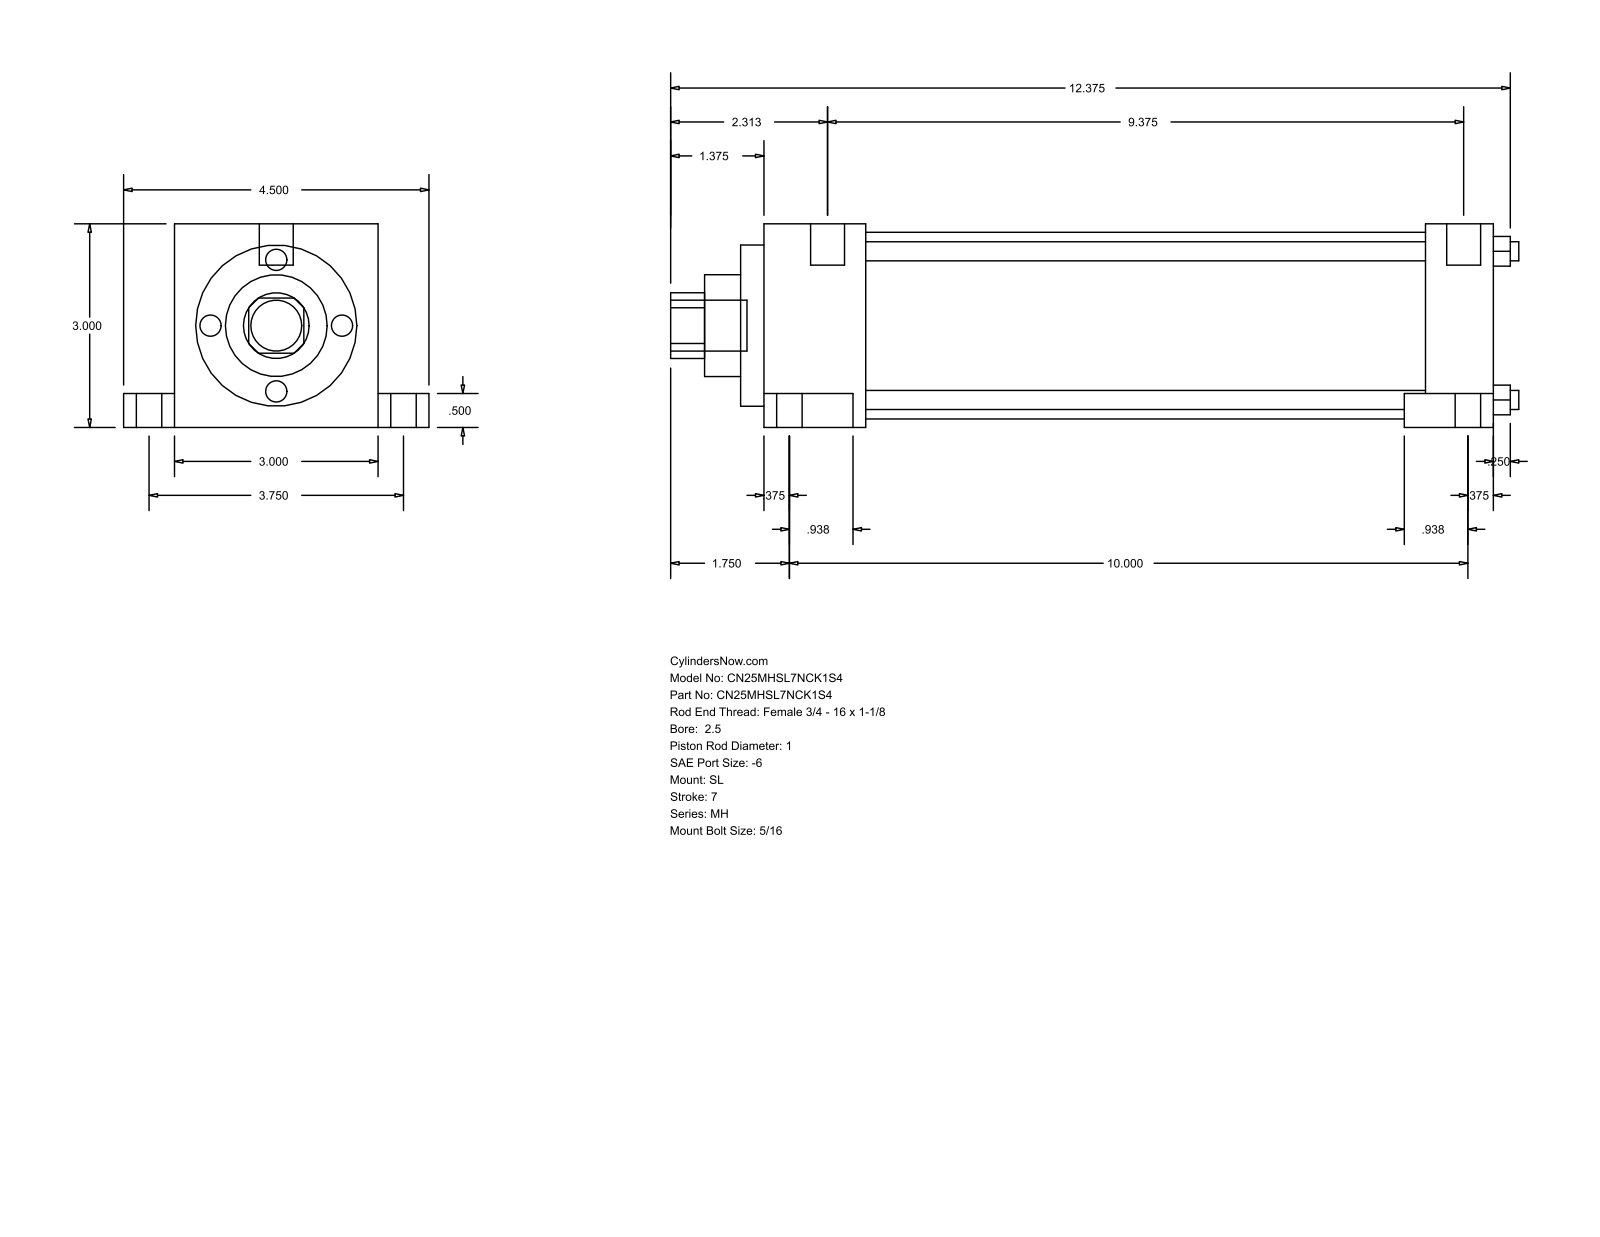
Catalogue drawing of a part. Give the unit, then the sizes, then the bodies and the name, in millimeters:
Units: millimetres
Overall size (bounding box): 317.5 × 114.3 × 76.2
Round holes (diameter × count): ⌀7.14 ×4, ⌀25.4 ×1, ⌀38.1 ×1, ⌀60.33 ×1, ⌀69.85 ×1
Round bosses / shafts (diameter × count): ⌀15.88 ×2, ⌀9.53 ×2, ⌀5.56 ×2, ⌀19.05 ×1, ⌀12.7 ×1
Partial cylindrical surfaces — rounded edges, fillets, slot ends (radius × count): R12.29 ×1
Main face-to-face distances: 76.2, 25.41, 256.38, 281.79, 12.7, 63.5, 19.05, 95.25, 13.49, 269.87
Hole centre spacings: 39.33, 55.62, 78.66
Bodies: 0 solids, 86 faces (61 planar, 25 cylindrical, 0 other)
Part name (STEP PRODUCT): MH_SL__0250_1
STEP written by: GSSL Pune (CONFIG_CONTROL_DESIGN)
